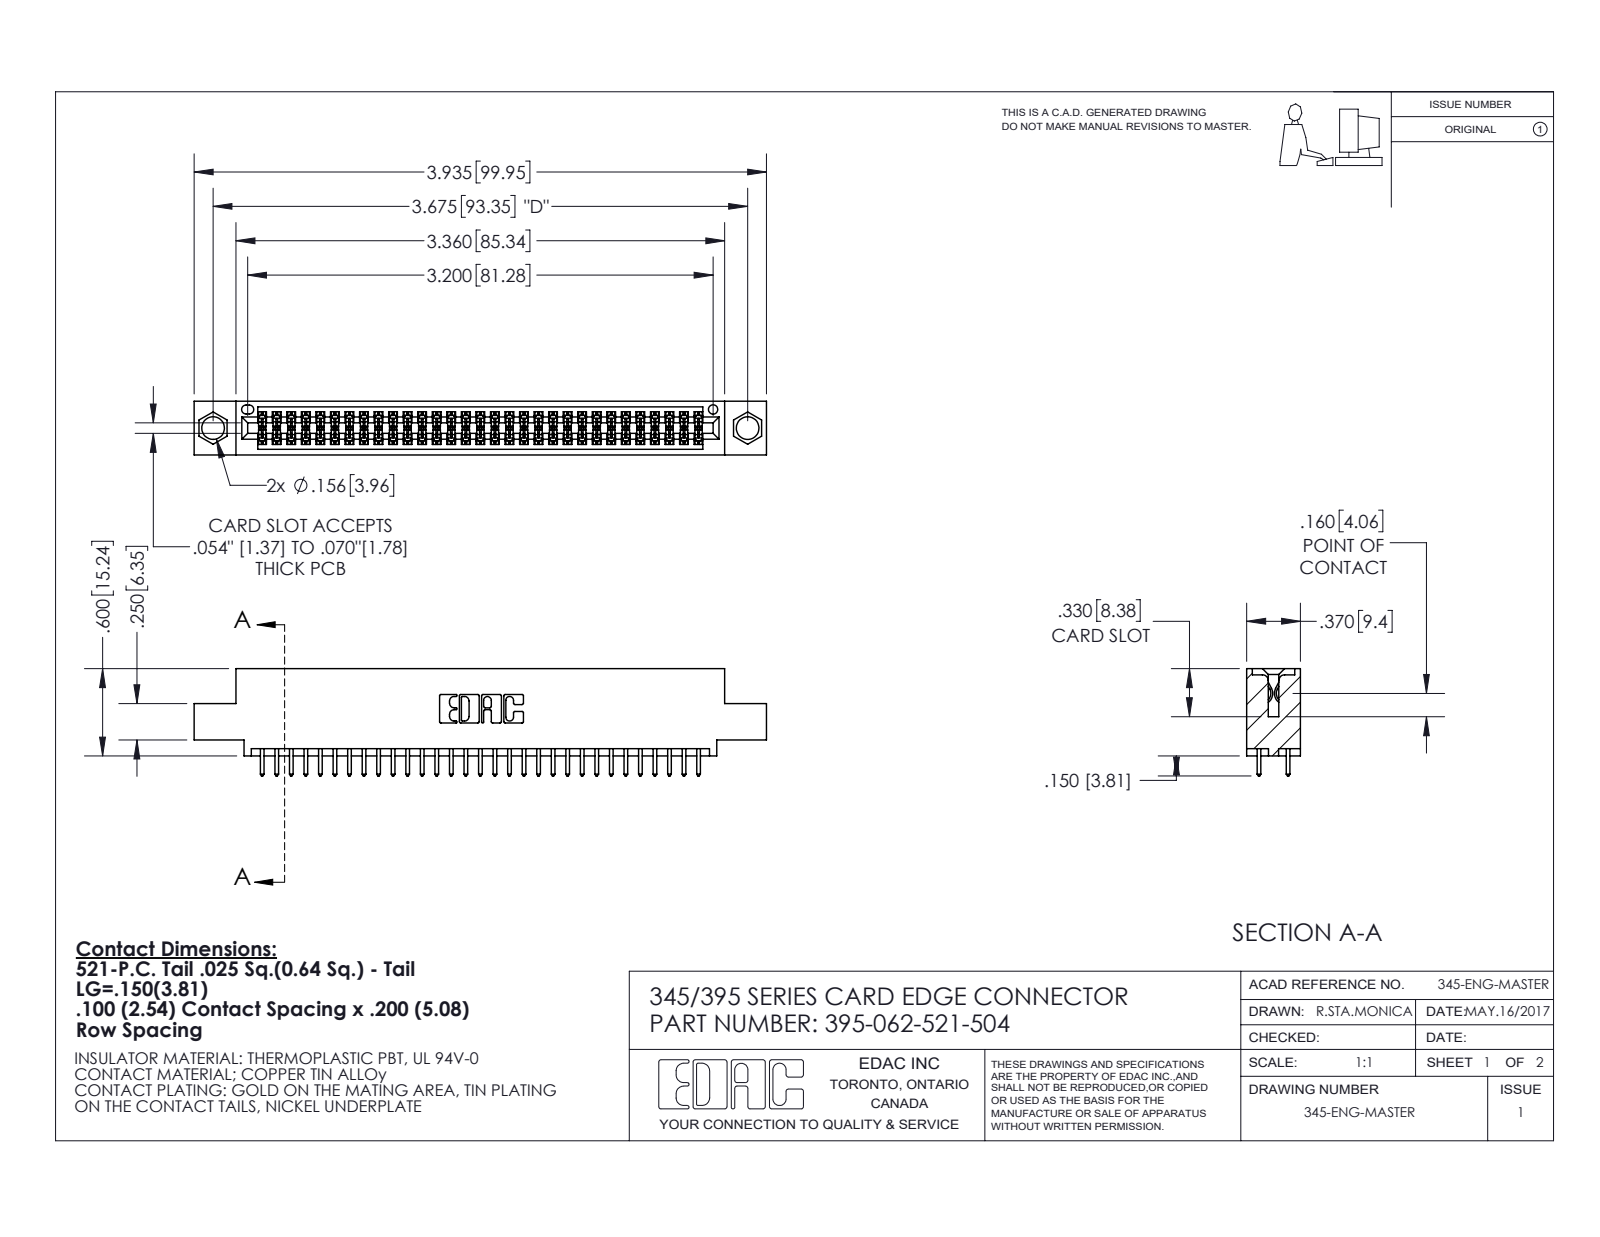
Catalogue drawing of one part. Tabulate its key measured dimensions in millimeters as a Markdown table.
| quantity | value |
| --- | --- |
| part name | 345-292-001_345-293-121; 395-062-521-504; 345 Part_0.110 Offset - 0.156 Dia-TI |
| STEP written by | SolidWorks 2020 (CONFIG_CONTROL_DESIGN) |
| units | millimeters |
| bodies | 63 solids, 3244 faces (2144 planar, 1100 cylindrical, 0 other) |
| overall size | 99.9 × 18.7 × 9.4 |
| volume | 9 410 mm³ |
| surface area | 13 460 mm² |
| round holes (diameter × count) | 4 × 2, 1.6 × 1 |
| partial cylindrical surfaces (radius × count) | 0.2 × 124, 0.3 × 62, 0.3 × 22, 0.2 × 6, 0.8 × 6, 0.7 × 3, 0.4 × 2, 0.5 × 2 |
| main face-to-face distances | 1.8, 7.6, 5.1, 9.4, 2.5, 6.9, 0.6, 5.7, 4.4, 3.8 |
| hole center spacings | 6.9, 87.4, 93.3 |
